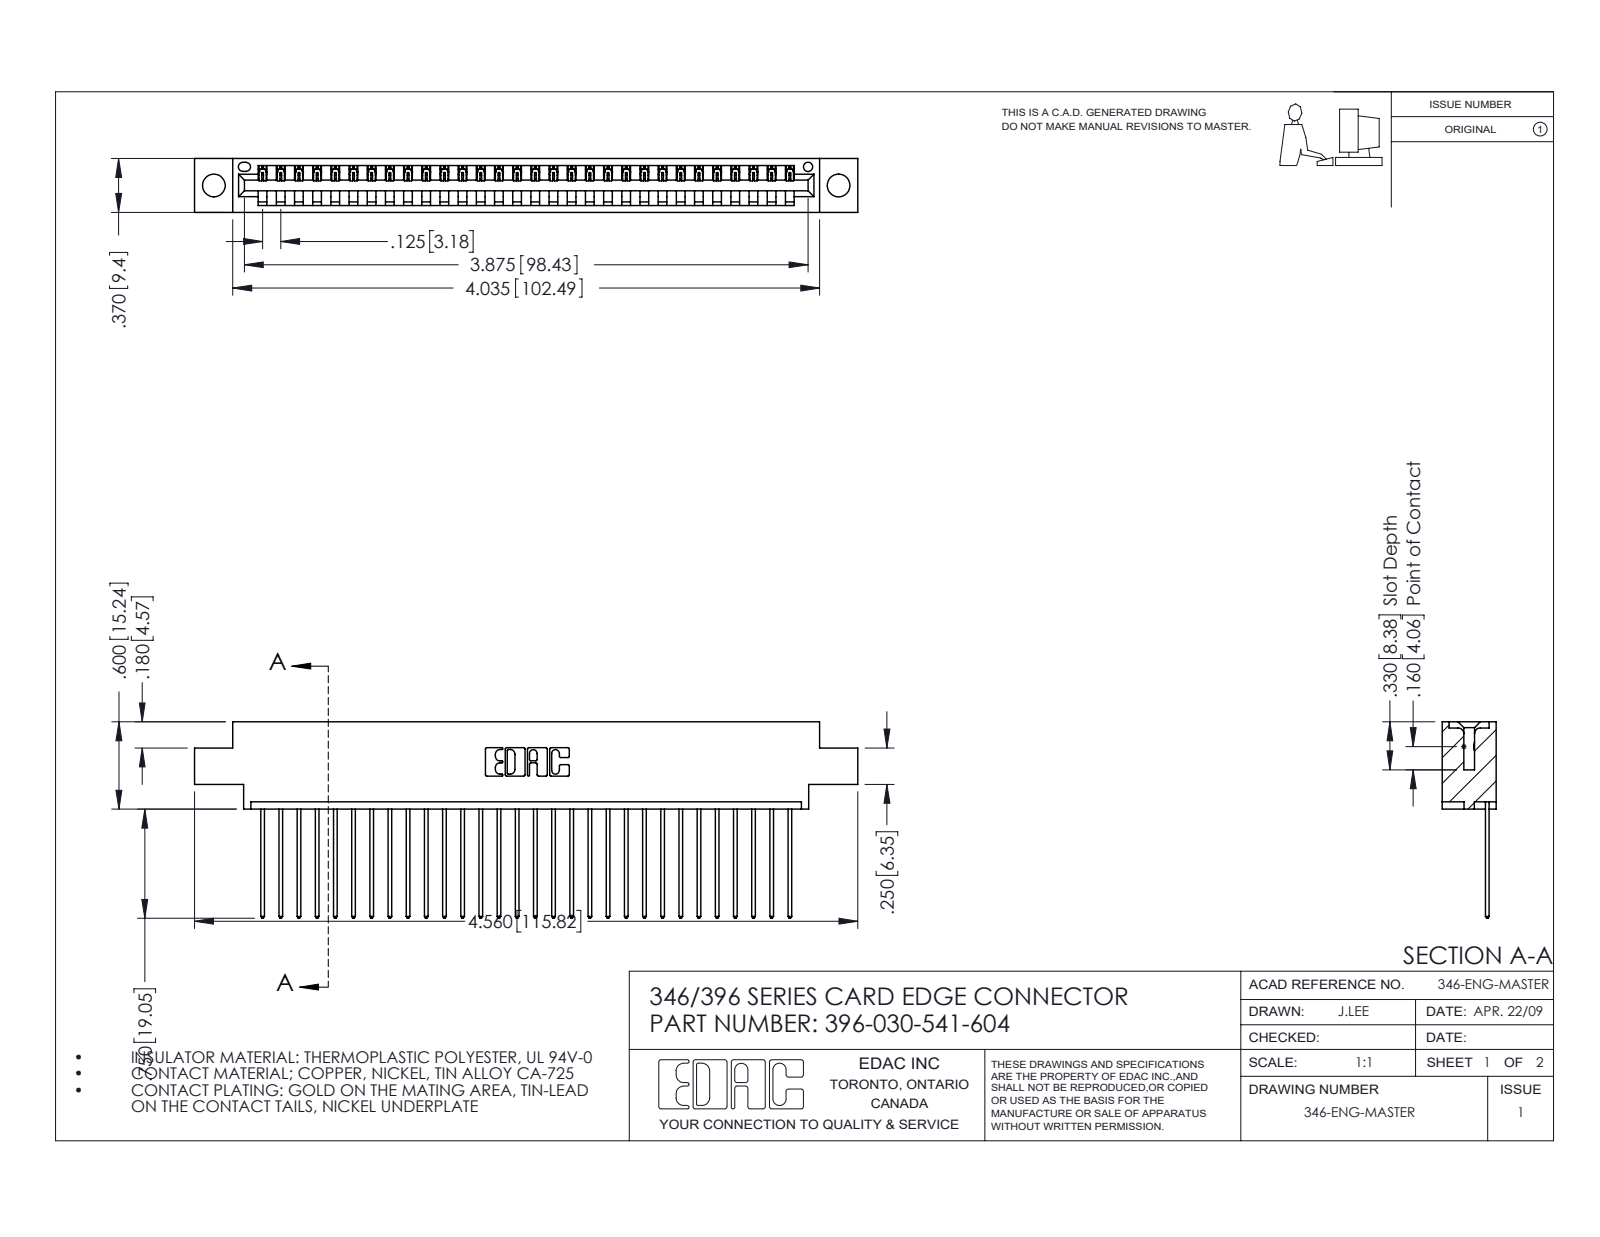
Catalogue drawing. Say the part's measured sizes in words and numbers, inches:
The part is named "345-292-001_345-293-141; 396-030-541-604; 346 Part_0.170 Offset - 0.156 Dia-TH". Its 3-D file was written by "SolidWorks 2016 (CONFIG_CONTROL_DESIGN)". It is 31 solids with 1866 faces: 1280 planar, 586 cylindrical and 0 other. Overall it measures 4.56 by 1.35 by 0.37 inches. Its volume is 0.663 cubic inches and its surface area 21.7 square inches. Round holes: 2 of diameter 0.156, 1 of diameter 0.064. Partial cylindrical surfaces (rounded edges, fillets, slot ends): 60 of radius 0.006, 60 of radius 0.01, 22 of radius 0.01, 6 of radius 0.007, 6 of radius 0.031, 3 of radius 0.026, 2 of radius 0.031, 2 of radius 0.04. The main face-to-face distances are 0.048, 0.322, 0.37, 0.25, 0.072, 0.298, 0.025, 0.148, 0.222, 0.1. The hole center spacings are 0.246, 4.087, 4.295.
